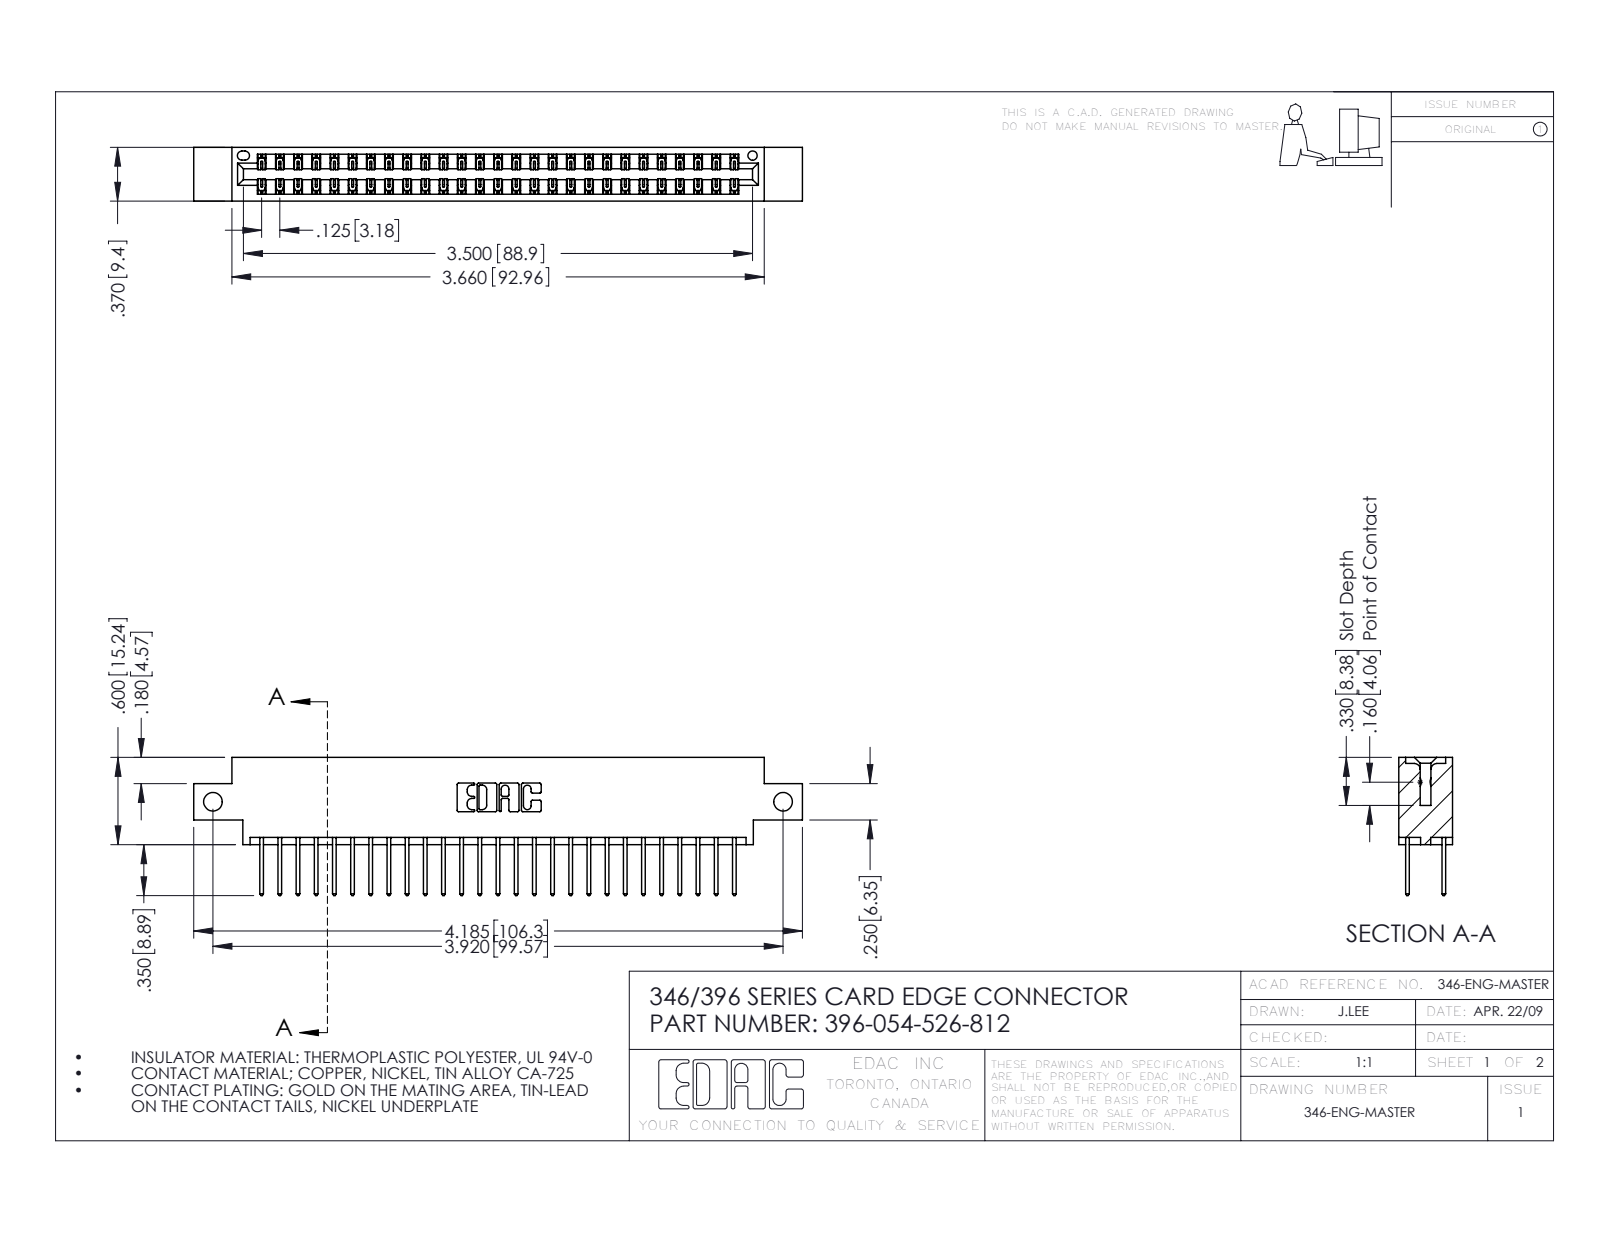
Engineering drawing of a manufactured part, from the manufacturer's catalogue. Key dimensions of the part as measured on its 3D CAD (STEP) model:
Part name (STEP PRODUCT): 345-292-001_345-293-126; 396-054-526-812; 346 Part_0.170 Offset - Side Mount
STEP written by: SolidWorks 2016 (CONFIG_CONTROL_DESIGN)
Units: inches
Bodies: 55 solids, 2934 faces (1970 planar, 964 cylindrical, 0 other)
Overall size (bounding box): 4.185 × 0.95 × 0.37
Volume: 0.616 in³ · Surface area: 21.82 in²
Round holes (diameter × count): ⌀0.128 ×2, ⌀0.064 ×1
Partial cylindrical surfaces — rounded edges, fillets, slot ends (radius × count): R0.006 ×81, R0.01 ×54, R0.01 ×22, R0.007 ×6, R0.031 ×6, R0.026 ×3, R0.014 ×2, R0.022 ×2
Main face-to-face distances: 0.048, 0.322, 0.25, 0.37, 0.072, 0.298, 0.025, 0.275, 0.148, 0.222
Hole centre spacings: 3.92
